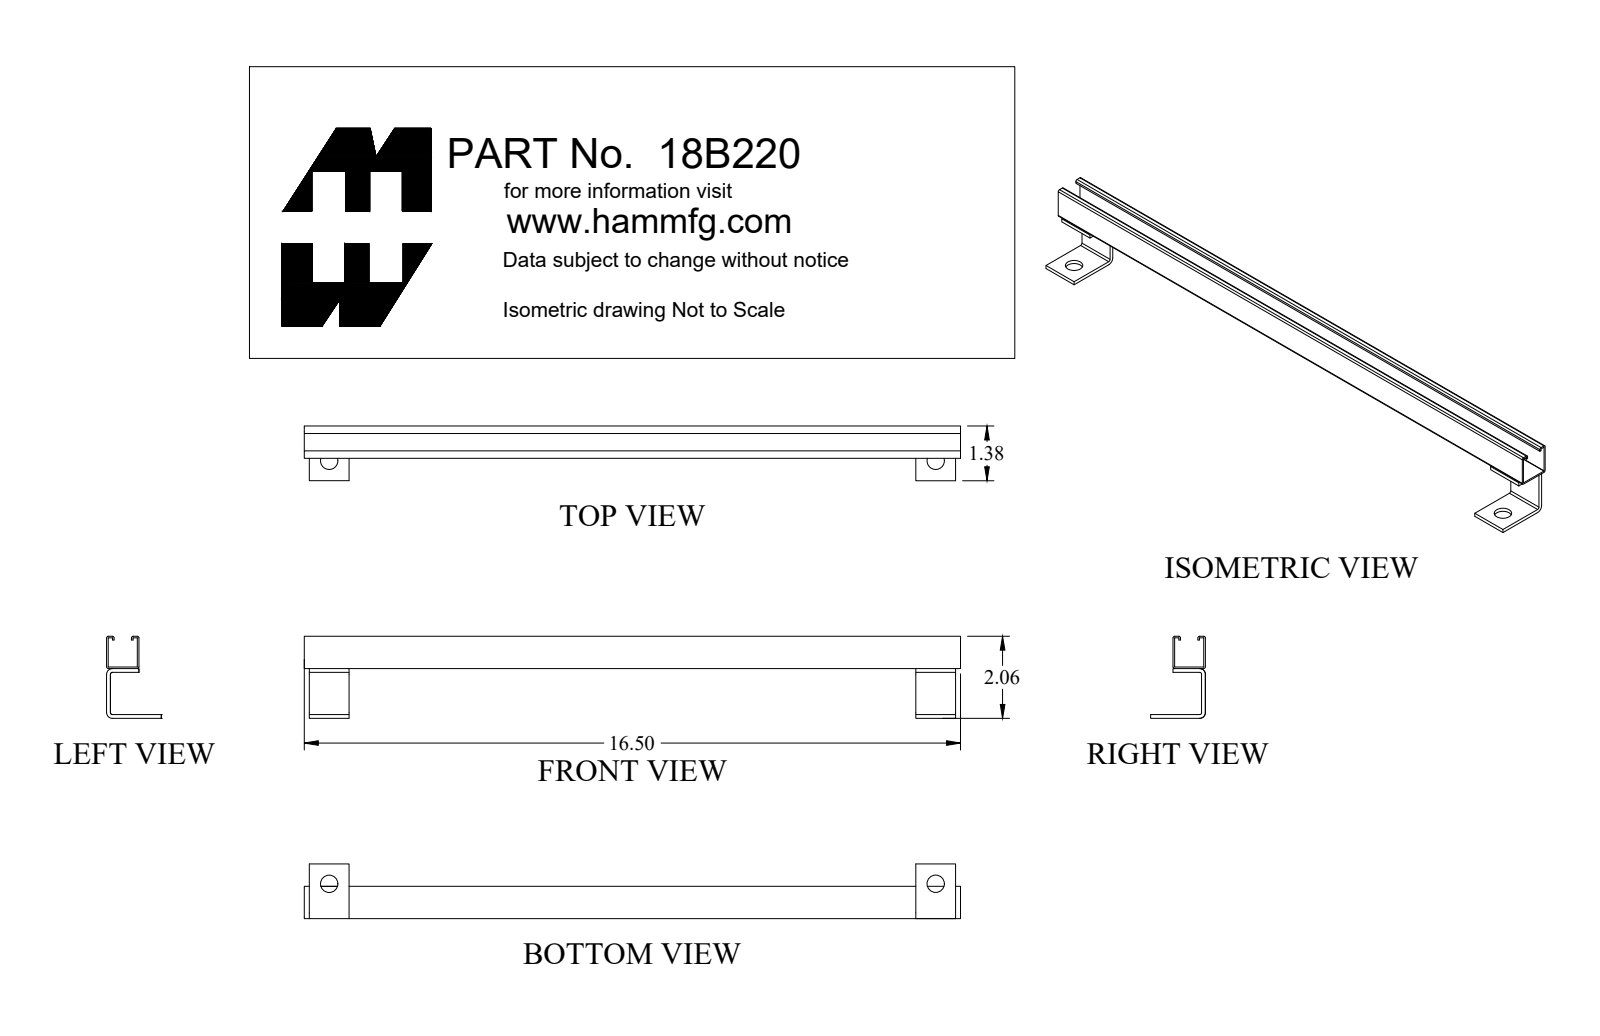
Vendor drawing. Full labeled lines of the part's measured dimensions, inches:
Part name (STEP PRODUCT): 18B220
STEP written by: SolidWorks 2018 (AUTOMOTIVE_DESIGN)
Units: inches
Bodies: 3 solids, 60 faces (38 planar, 22 cylindrical, 0 other)
Overall size (bounding box): 16.5 × 2.063 × 1.376
Volume: 2.357 in³ · Surface area: 104.7 in²
Round holes (diameter × count): ⌀0.437 ×2
Partial cylindrical surfaces — rounded edges, fillets, slot ends (radius × count): R0.043 ×6, R0.048 ×4, R0.143 ×4
Main face-to-face distances: 0.04, 0.773, 0.813, 0.733, 0.773, 0.095, 1.155, 0.813, 0.733, 0.148
Hole centre spacings: 11.25
